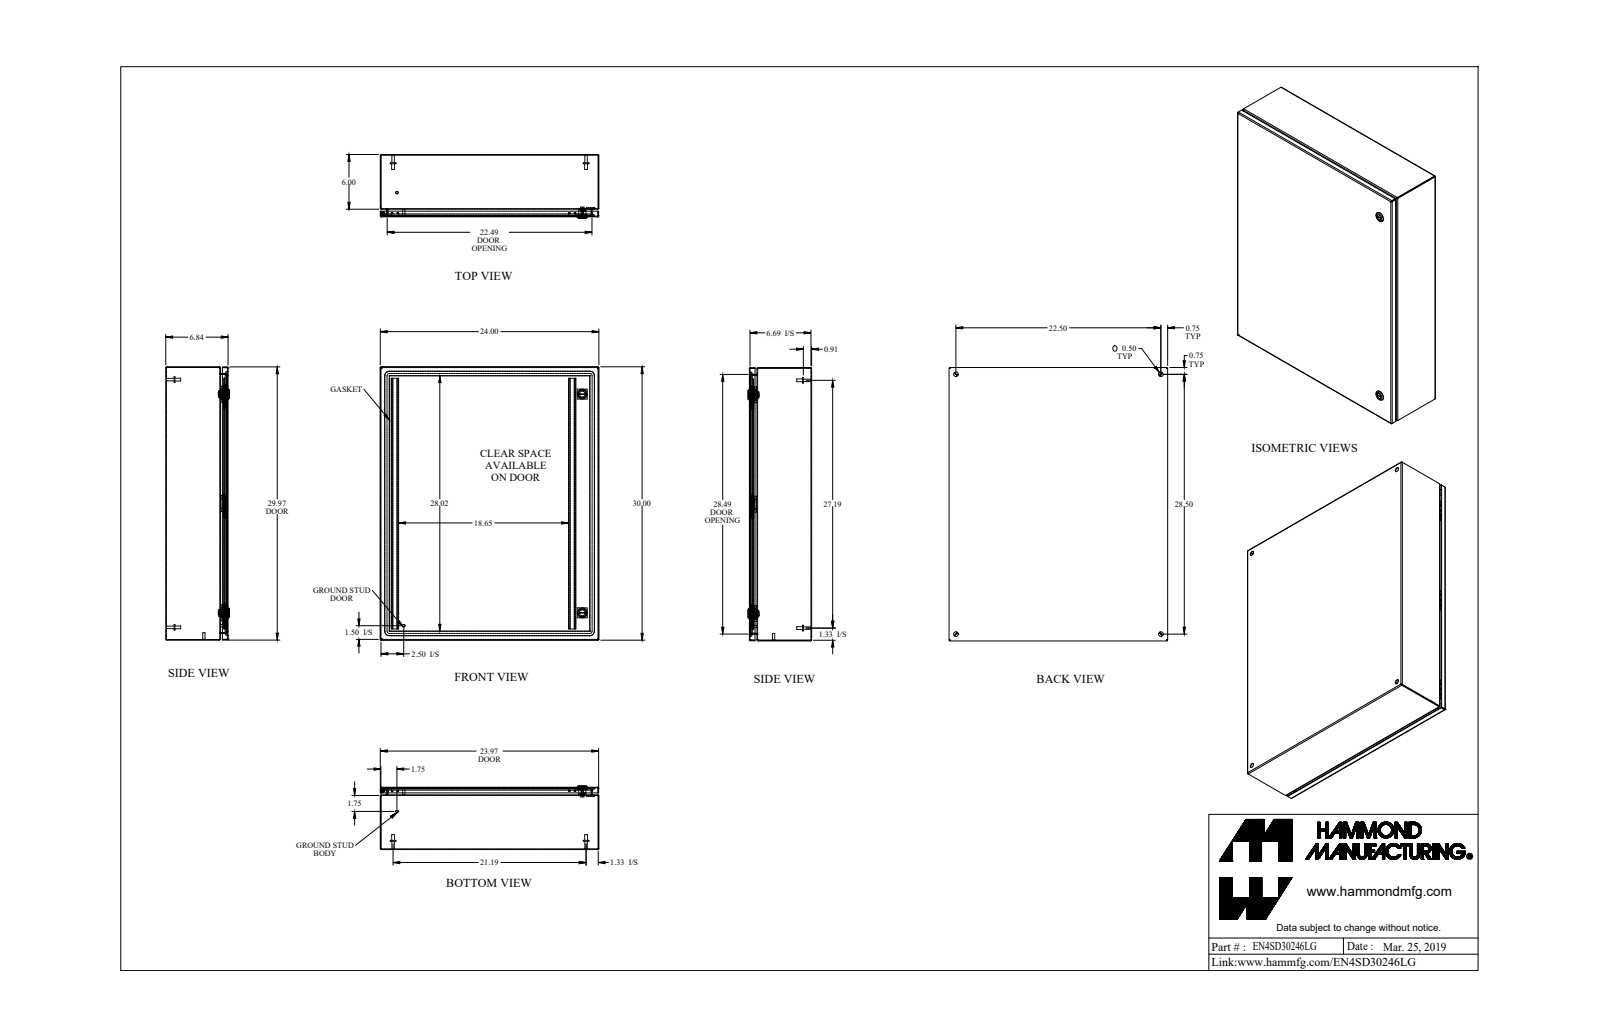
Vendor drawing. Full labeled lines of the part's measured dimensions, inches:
Part name (STEP PRODUCT): EN4SD30246LG_Default
STEP written by: SolidWorks 2019 (CONFIG_CONTROL_DESIGN)
Units: inches
Bodies: 31 solids, 885 faces (422 planar, 295 cylindrical, 168 other)
Overall size (bounding box): 30 × 24 × 6.997
Volume: 180 in³ · Surface area: 5 053 in²
Round holes (diameter × count): ⌀0.5 ×4, ⌀0.232 ×2, ⌀0.625 ×2, ⌀0.785 ×2, ⌀0.172 ×1, ⌀0.24 ×1, ⌀0.242 ×1
Round bosses / shafts (diameter × count): ⌀0.625 ×4, ⌀0.313 ×4, ⌀0.27 ×4, ⌀1.1 ×2, ⌀0.525 ×2, ⌀0.281 ×2, ⌀0.25 ×2, ⌀0.455 ×1
Partial cylindrical surfaces — rounded edges, fillets, slot ends (radius × count): R0.036 ×20, R0.108 ×20, R0.043 ×12, R0.081 ×12, R0.382 ×12, R19.003 ×8, R0.006 ×6, R0.062 ×6
Main face-to-face distances: 0.072, 6.765, 6.693, 6.837, 23.928, 29.928, 23.856, 24, 29.856, 30
Hole centre spacings: 22.5, 28.5, 36.311, 2.493, 2.494, 21.545, 21.545, 23.999
